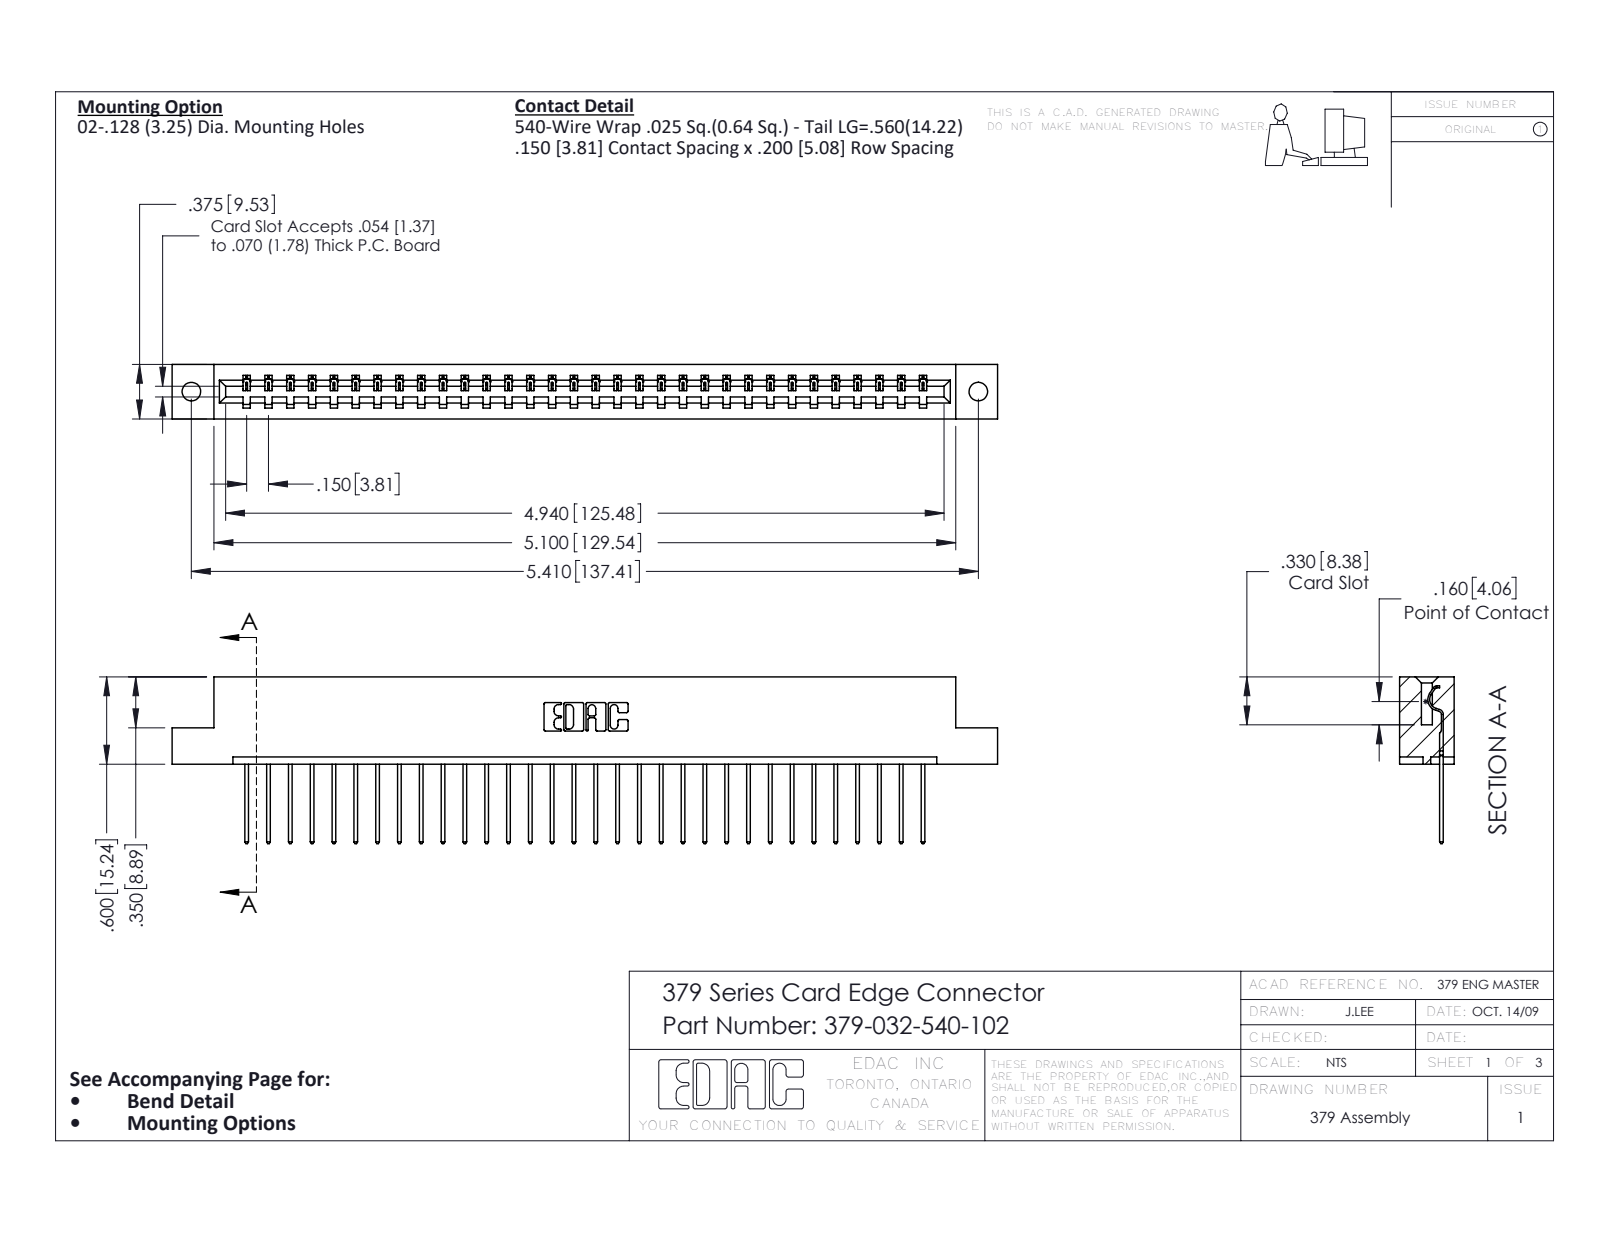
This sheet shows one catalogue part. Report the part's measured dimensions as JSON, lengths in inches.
{"part_name": "379-032-540-102; 345-292-001_345-293-140; 379 Part_Flush - .128 Dia", "step_written_by": "SolidWorks 2016 (CONFIG_CONTROL_DESIGN)", "units": "inches", "bodies": {"solids": 33, "faces": 1970, "planar": 1414, "cylindrical": 556, "other": 0}, "overall_size": [5.675, 1.147, 0.375], "volume_in3": 0.917, "surface_area_in2": 23.84, "round_holes": [[0.128, 2]], "partial_cylinders_radius": [[0.006, 64], [0.01, 64], [0.01, 22], [0.007, 6], [0.031, 6], [0.026, 3], [0.014, 1], [0.022, 1]], "face_to_face_distances": [0.3, 0.075, 0.375, 0.225, 0.275, 0.2, 0.1, 0.025, 0.6, 0.55], "hole_center_spacings": [5.41]}
